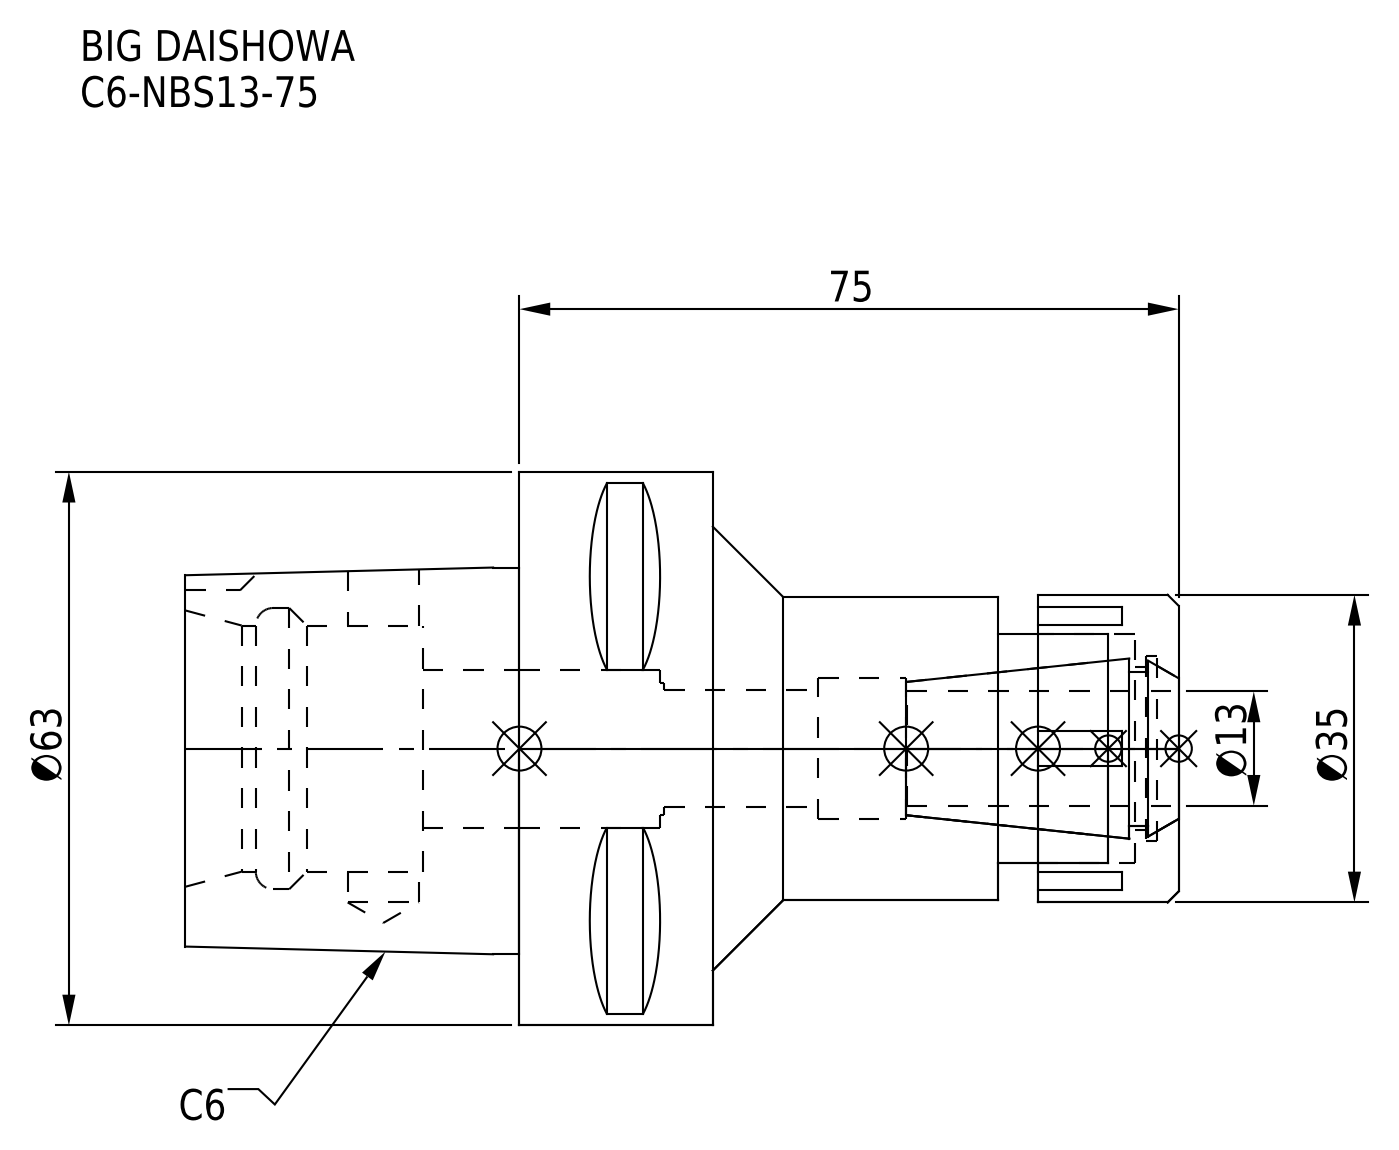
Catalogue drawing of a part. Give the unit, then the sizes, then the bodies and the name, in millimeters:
Units: millimetres
Overall size (bounding box): 113 × 63 × 63
Round holes (diameter × count): ⌀8.1 ×1, ⌀13.3 ×1, ⌀15 ×1, ⌀16 ×1, ⌀18 ×1, ⌀18.5 ×1, ⌀21 ×1, ⌀26 ×1, ⌀28 ×1, ⌀32 ×1
Round bosses / shafts (diameter × count): ⌀63 ×1, ⌀35 ×1, ⌀34.5 ×1
Partial cylindrical surfaces — rounded edges, fillets, slot ends (radius × count): R5 ×1
Main face-to-face distances: 22, 53, 75, 11, 70, 38, 113, 60, 20.5, 16
Volume: 134 986 mm³ · Surface area: 31 185 mm²
Bodies: 2 solids, 112 faces (61 planar, 33 cylindrical, 18 other)
Part name (STEP PRODUCT): NBN13_1.stp; C6-NBS13-75-130_ASM.stp; DXF_TEMP_ASSY_ASM_4_ASM.stp; C6-NBS13-75.stp (+3 more)
STEP written by: SolidWorks 2019 (CONFIG_CONTROL_DESIGN)
